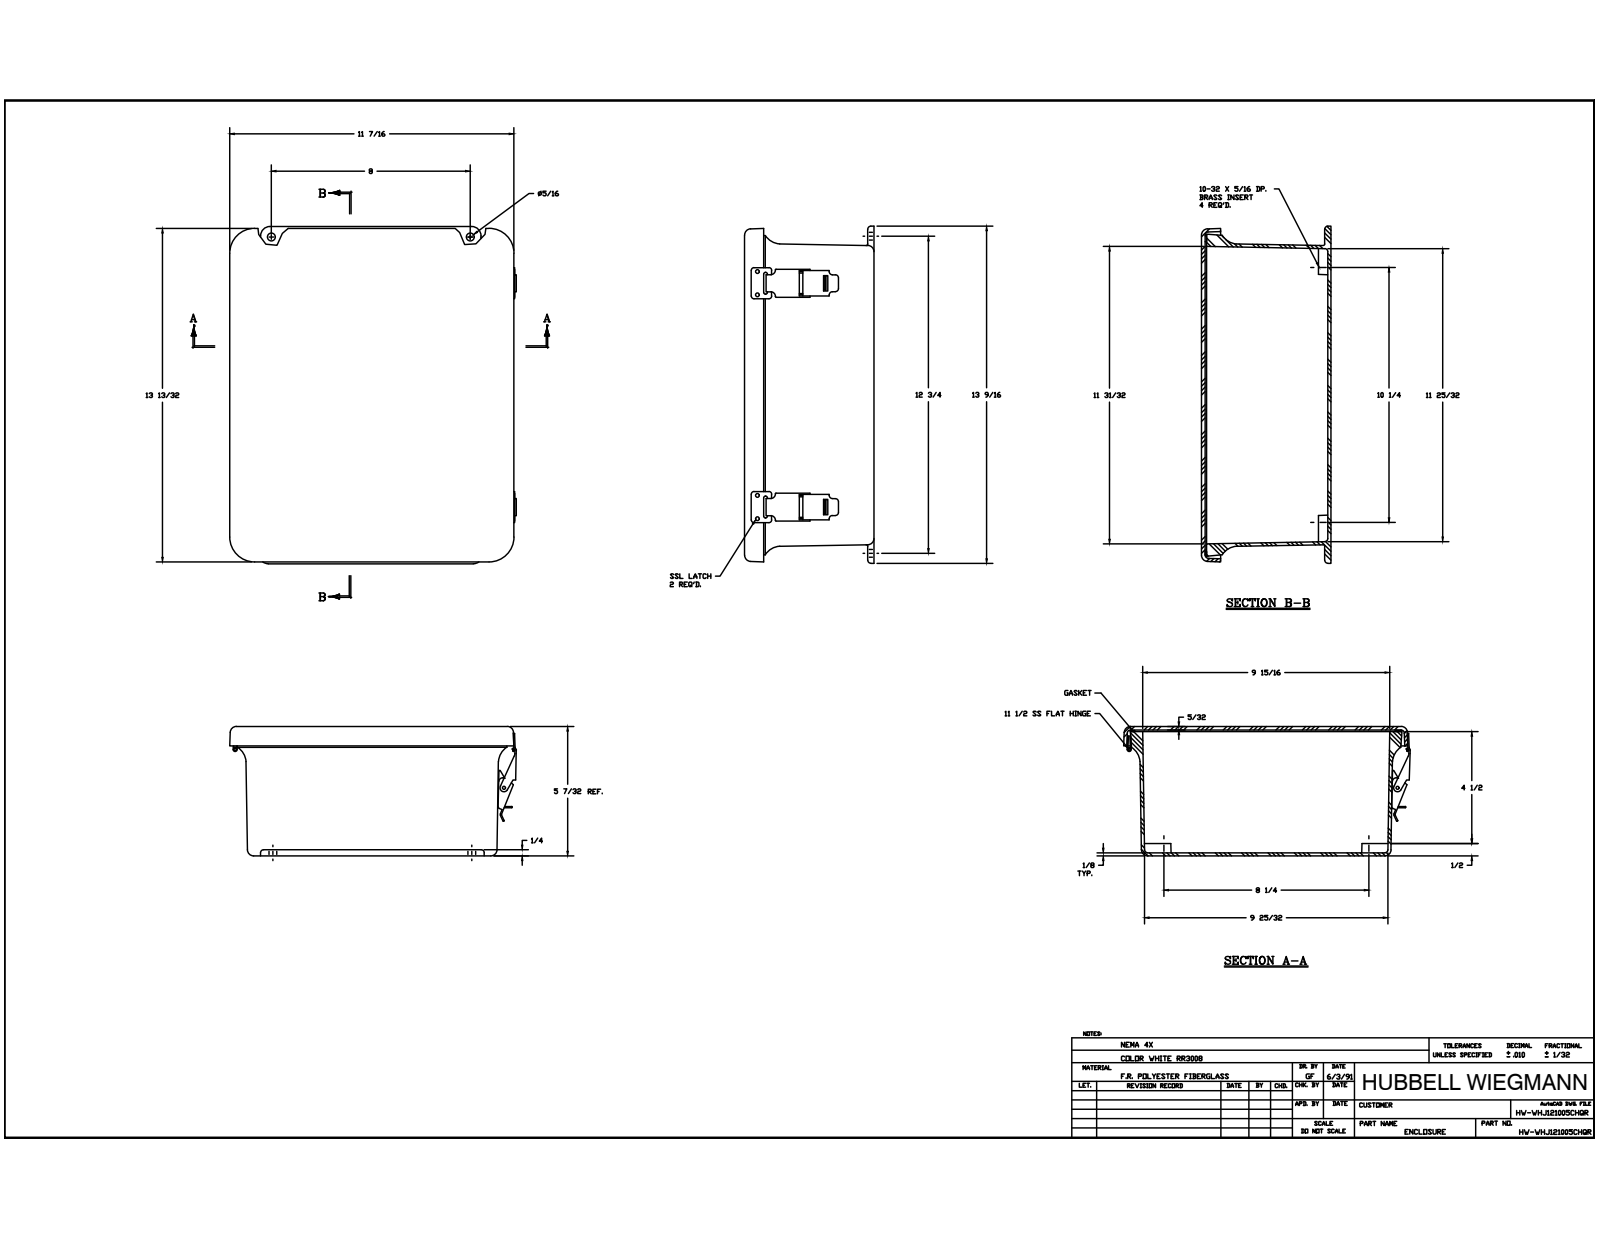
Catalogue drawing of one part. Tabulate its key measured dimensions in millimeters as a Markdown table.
| quantity | value |
| --- | --- |
| part name | J1210HL_1; RMINS45821P_101; RMINS45821P_102; RMINS45821P_103 (+8 more) |
| STEP written by | Autodesk Inventor 2014 (AUTOMOTIVE_DESIGN) |
| units | millimeters |
| bodies | 38 solids, 979 faces (423 planar, 409 cylindrical, 147 other) |
| overall size | 344.49 × 293.04 × 132.86 |
| volume | 1 430 000 mm³ |
| surface area | 772 921 mm² |
| round holes (diameter × count) | 3.56 × 20, 2.64 × 8, 3.33 × 8, 3.86 × 5, 3.3 × 4, 3.96 × 4, 5.54 × 4, 3.43 × 2, 9.52 × 2, 2.16 × 1, 2.16 × 1 |
| round bosses / shafts (diameter × count) | 3.17 × 16, 6.35 × 8, 6.86 × 4, 7.62 × 1, 4.31 × 1, 3.94 × 1, 3.05 × 1 |
| partial cylindrical surfaces (radius × count) | 0.38 × 20, 0.79 × 20, 3.17 × 20, 1.14 × 16, 0.76 × 12, 0.57 × 9, 6.35 × 8, 1.52 × 6 |
| main face-to-face distances | 3.63, 3.18, 129.23, 132.86, 126.05, 129.68, 127, 123.82, 2.23, 5.86 |
| hole center spacings | 228.6, 229.39, 23.81, 19.05, 92.08, 6.35, 19.04, 34.24 |
